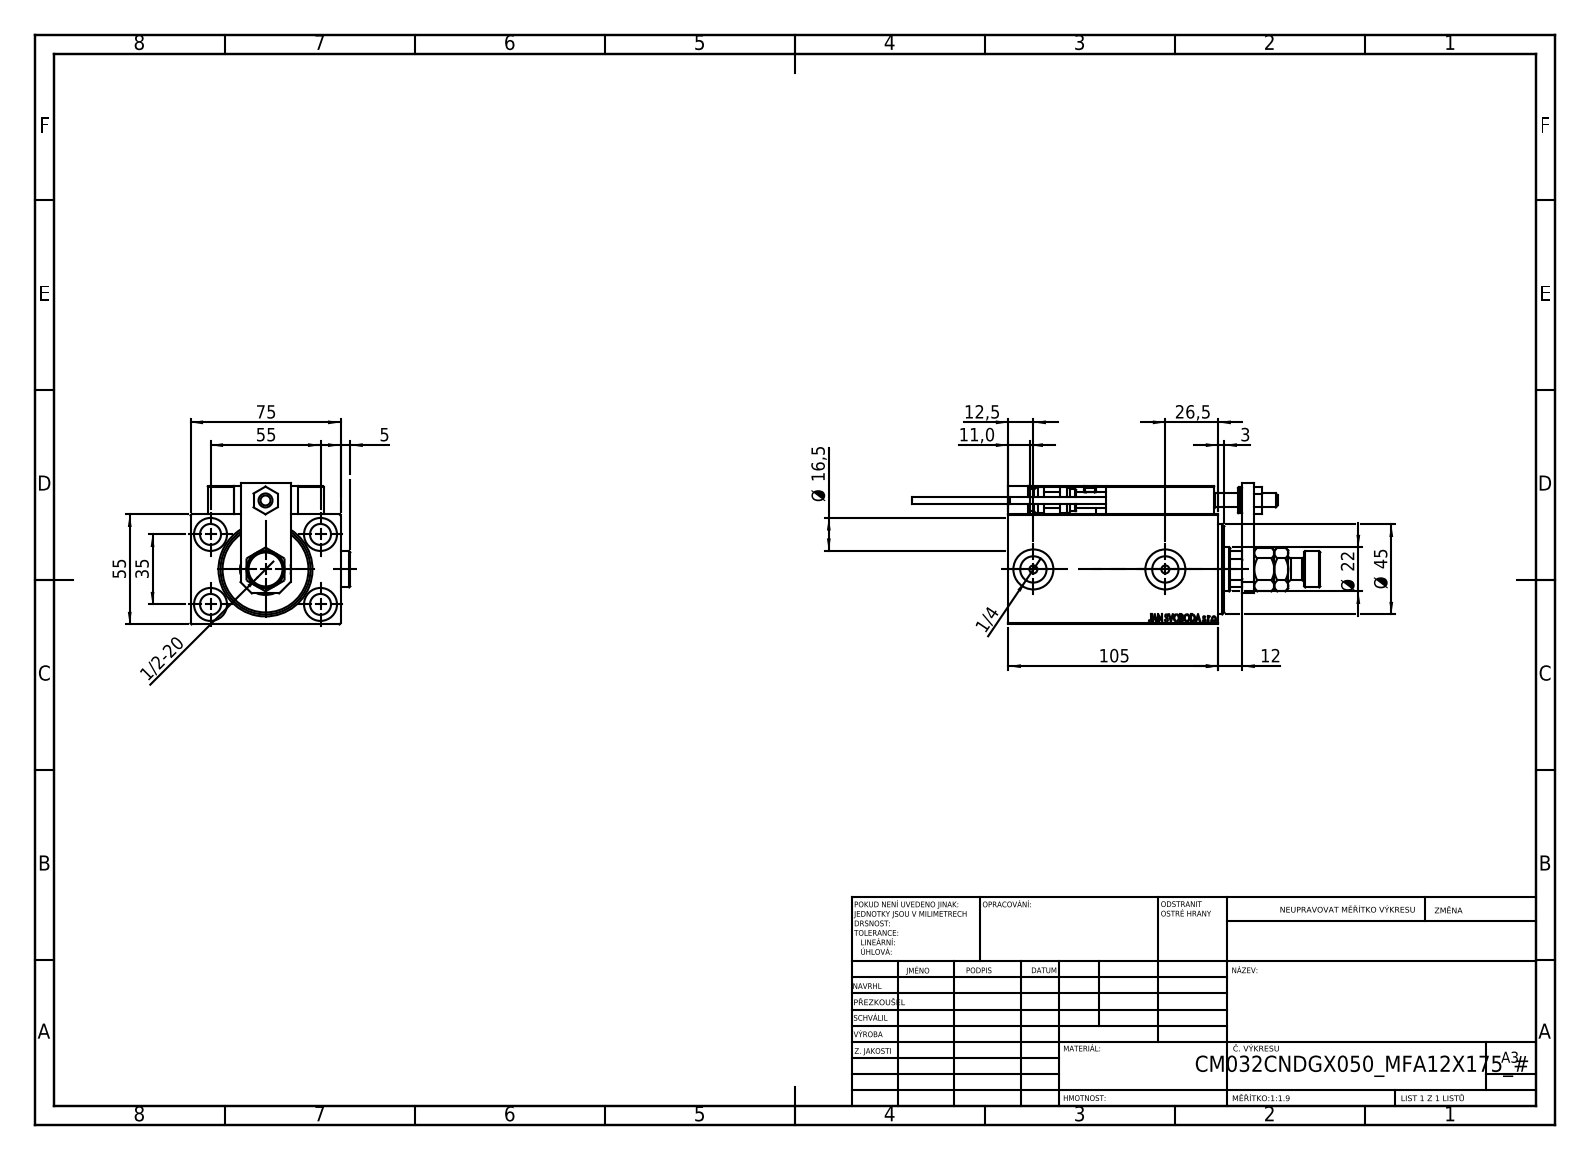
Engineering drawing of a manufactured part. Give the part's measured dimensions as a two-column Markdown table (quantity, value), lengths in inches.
| quantity | value |
| --- | --- |
| part name | NUT_D12; ALLEN BOLT D5; SWITCH DIM B,W; V450CM_C_Body (+7 more) |
| STEP written by | SolidWorks 2019 (CONFIG_CONTROL_DESIGN) |
| units | inches |
| bodies | 26 solids, 1388 faces (610 planar, 208 cylindrical, 570 other) |
| overall size | 8.031 × 3.146 × 2.776 |
| volume | 25.75 in³ |
| surface area | 166.9 in² |
| round holes (diameter × count) | 0.157 × 6, 0.315 × 5, 0.413 × 5, 0.65 × 5, 0.126 × 4, 0.197 × 2, 0.518 × 2, 0.787 × 2, 0.276 × 1, 0.866 × 1, 1.004 × 1, 1.26 × 1 |
| round bosses / shafts (diameter × count) | 0.709 × 3, 0.433 × 2, 0.197 × 2, 0.15 × 2, 0.512 × 1 |
| partial cylindrical surfaces (radius × count) | 0.012 × 30, 0.118 × 2, 0.413 × 1 |
| main face-to-face distances | 2.165, 2.953, 0.551, 0.394, 0.472, 0.197, 2.717, 0.118, 0.276, 0.591 |
| hole center spacings | 1.283, 0.448, 0.787, 1.165, 1.169, 1.273, 1.378, 1.42 |
